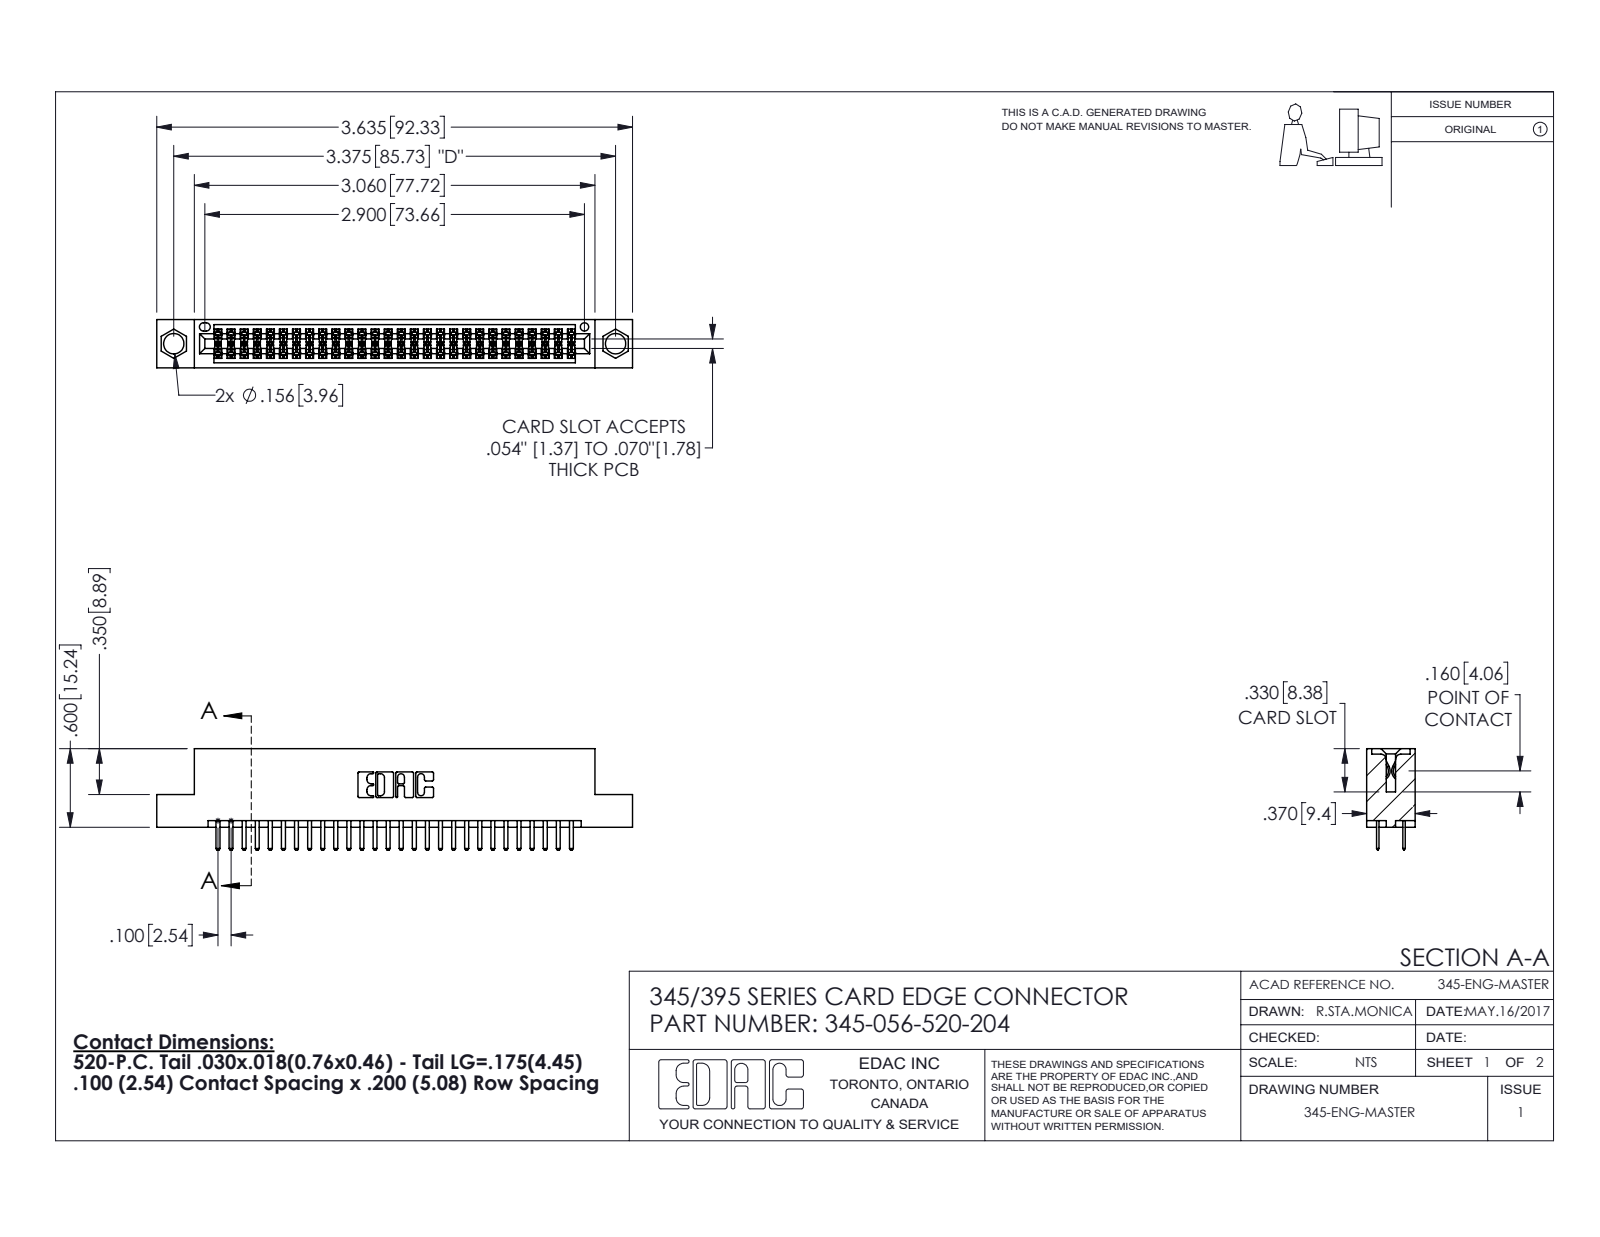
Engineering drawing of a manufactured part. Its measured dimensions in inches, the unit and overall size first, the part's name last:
Units: inches
Overall size (bounding box): 3.635 × 0.775 × 0.37
Round holes (diameter × count): ⌀0.156 ×2, ⌀0.064 ×1
Partial cylindrical surfaces — rounded edges, fillets, slot ends (radius × count): R0.006 ×84, R0.01 ×60, R0.01 ×22, R0.007 ×6, R0.031 ×6, R0.026 ×3, R0.014 ×2, R0.019 ×2
Main face-to-face distances: 0.298, 0.072, 0.2, 0.37, 0.098, 0.272, 0.025, 0.225, 0.022, 0.072
Hole centre spacings: 0.27, 3.14, 3.375
Volume: 0.531 in³ · Surface area: 19.22 in²
Bodies: 57 solids, 3164 faces (2054 planar, 1110 cylindrical, 0 other)
Part name (STEP PRODUCT): 345-292-001_345-293-120; 345-056-520-204; 345 Part_Flush Mounting Lugs - 0.156 Dia-TI
STEP written by: SolidWorks 2020 (CONFIG_CONTROL_DESIGN)
